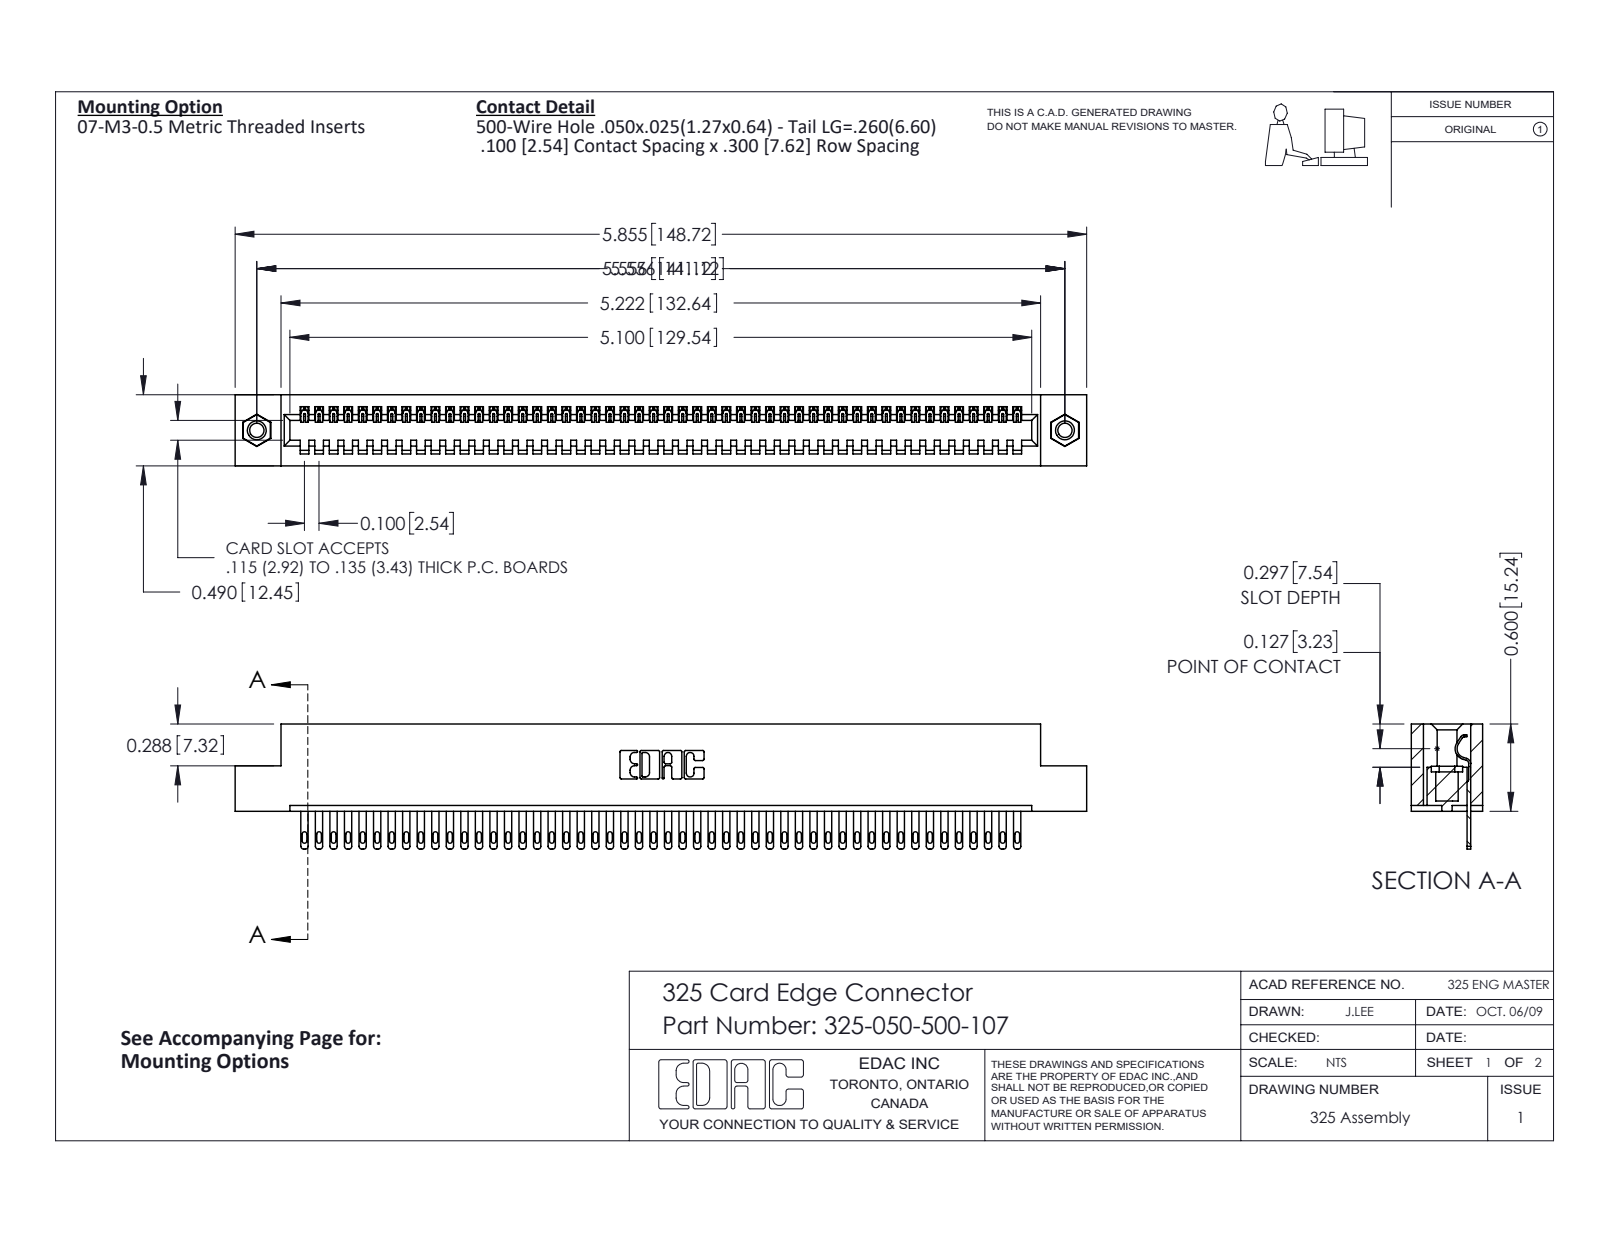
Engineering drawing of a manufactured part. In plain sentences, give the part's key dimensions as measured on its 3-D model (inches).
The part is named "325-050-500-107; 345-250-001_345-250-005-103; 325-292-001_325-293-100; 325 Part_TI". Its 3-D file was written by "SolidWorks 2016 (CONFIG_CONTROL_DESIGN)". It is 53 solids with 2874 faces: 1902 planar, 956 cylindrical and 16 other. Overall it measures 5.855 by 0.86 by 0.49 inches. Its volume is 1.157 cubic inches and its surface area 32.54 square inches. Round holes: 2 of diameter 0.098, 2 of diameter 0.125, 2 of diameter 0.16. Round bosses or shafts: 2 of diameter 0.155. Partial cylindrical surfaces (rounded edges, fillets, slot ends): 100 of radius 0.006, 100 of radius 0.016, 100 of radius 0.02, 22 of radius 0.01, 6 of radius 0.007, 6 of radius 0.031, 3 of radius 0.026, 1 of radius 0.014. The main face-to-face distances are 0.083, 0.407, 0.49, 0.3, 0.107, 0.383, 0.025, 0.325, 0.56, 0.263. The hole center spacings are 5.556.
